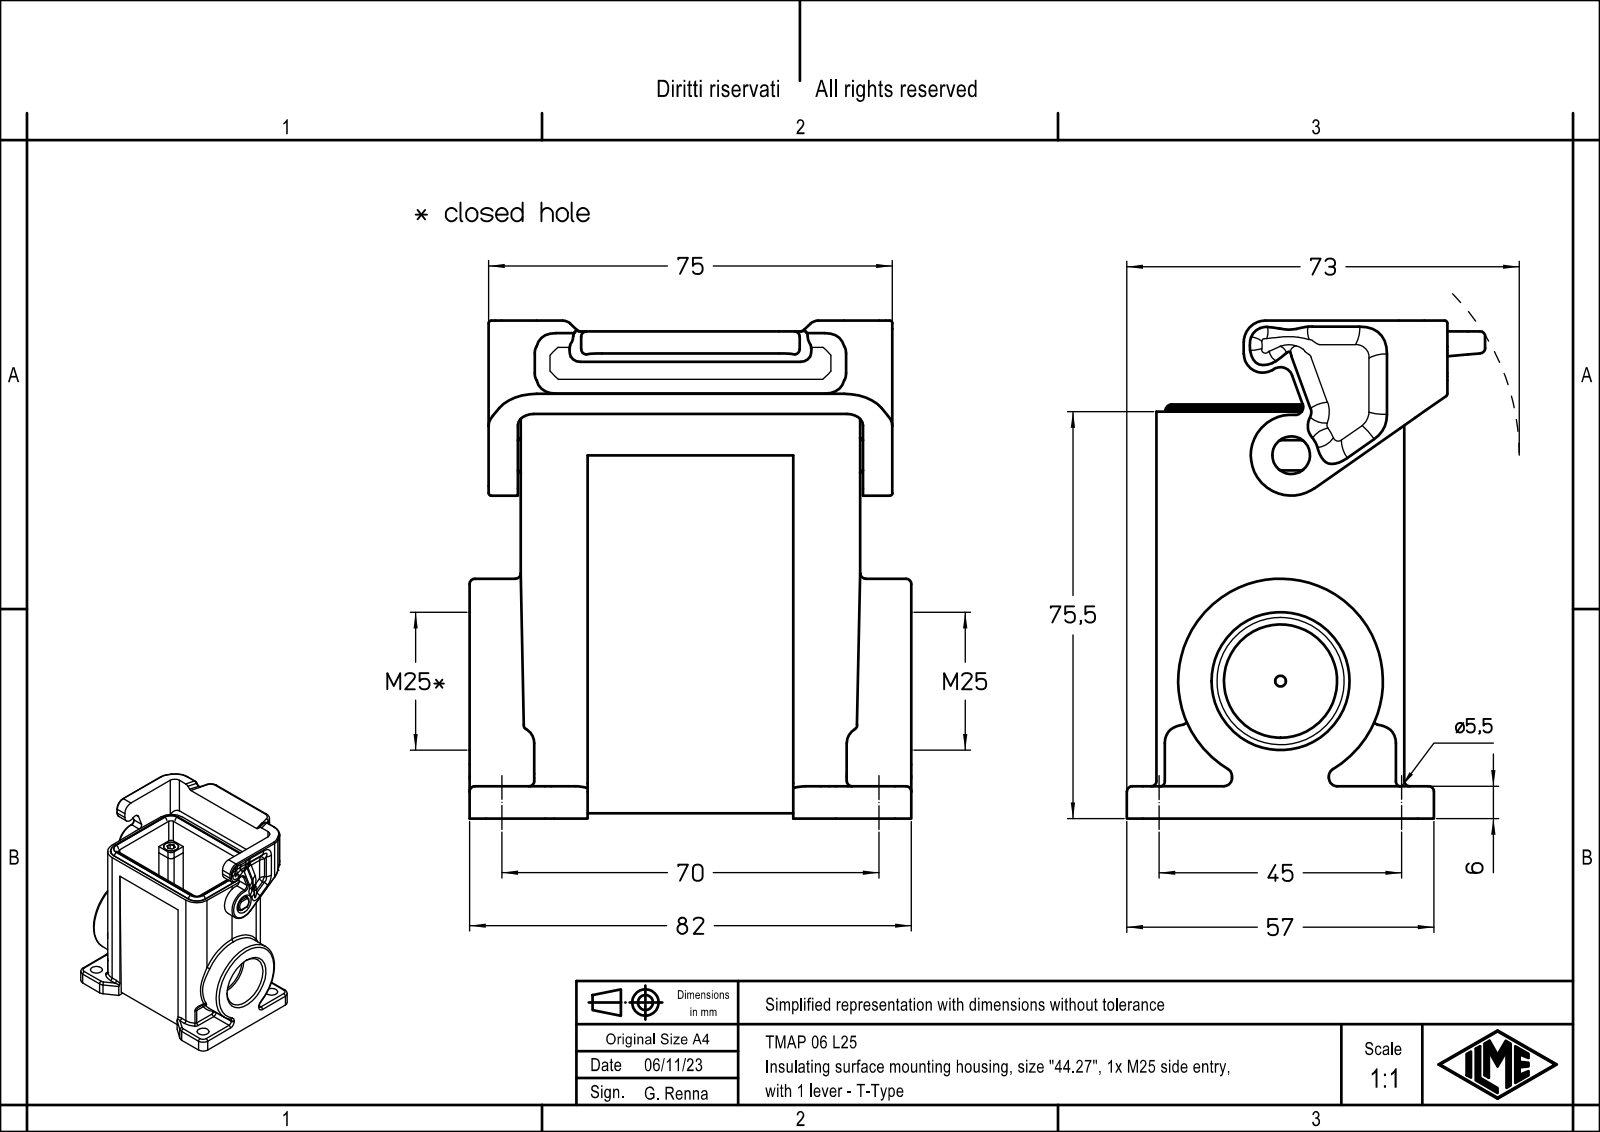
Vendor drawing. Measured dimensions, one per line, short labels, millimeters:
name: TMAP 06 L25
written by: Creo Elements/Direct Modeling 20.1B 02-Apr-2019 (C) Parametric Technology GmbH (AUTOMOTIVE_DESIGN)
unit: mm
bodies: 1 solid, 326 faces (162 planar, 128 cylindrical, 36 other)
size: 92.4 × 82 × 66.5
volume: 138 276 mm³; area: 47 533 mm²
holes: 4× ⌀5.5, 1× ⌀21, 1× ⌀23.6
bosses: 1× ⌀38
rounds: 17× R3, 10× R2, 9× R1.5, 8× R1, 8× R1.3, 4× R0.5, 4× R6, 4× R7
face distances: 5.4, 40.6, 46, 35.2, 5.5, 14.9, 1, 9, 67.1, 58.1
hole spacings: 45, 70, 83.22
